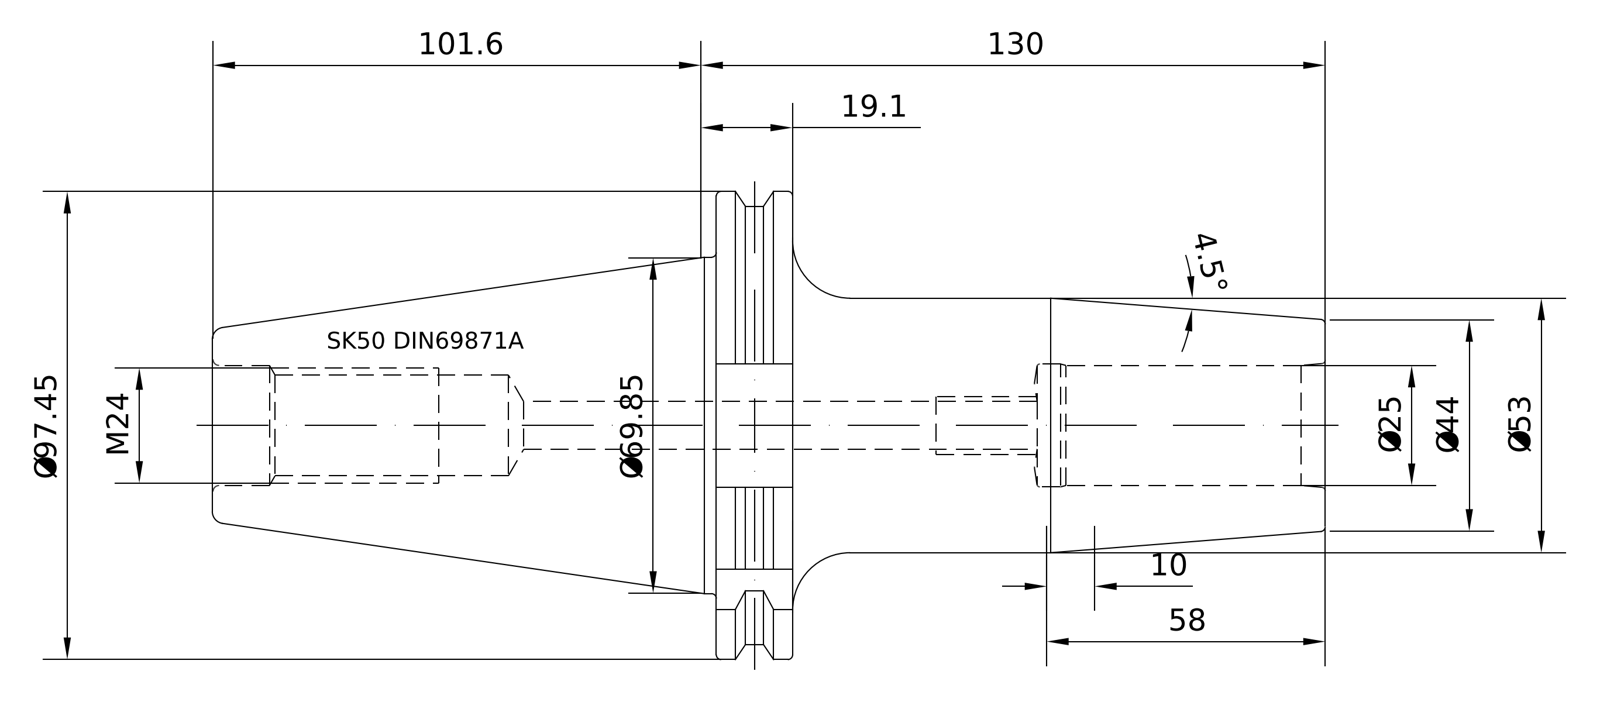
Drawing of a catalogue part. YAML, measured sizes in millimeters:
part_name: "50-444-25"
step_written_by: "PRO/ENGINEER BY PARAMETRIC TECHNOLOGY CORPORATION, 2010430 (CONFIG_CONTROL_DESIGN)"
units: millimeters
bodies: {solids: 1, faces: 94, planar: 22, cylindrical: 24, other: 48}
overall_size: [231.6, 97.47, 94]
volume: 541067
surface_area: 63368
round_holes:
  - {diameter: 20.75, count: 1}
  - {diameter: 25, count: 1}
  - {diameter: 25.01, count: 1}
  - {diameter: 25.7, count: 1}
round_bosses_or_shafts:
  - {diameter: 91, count: 1}
  - {diameter: 69.15, count: 1}
  - {diameter: 53, count: 1}
  - {diameter: 24.01, count: 1}
partial_cylinders:
  - {radius: 1.75, count: 1}
  - {radius: 48.74, count: 1}
face_to_face_distances: [15.85, 126.8, 110.95, 68.8, 52.95, 58, 72.8, 104.8, 120.65, 173.6]
